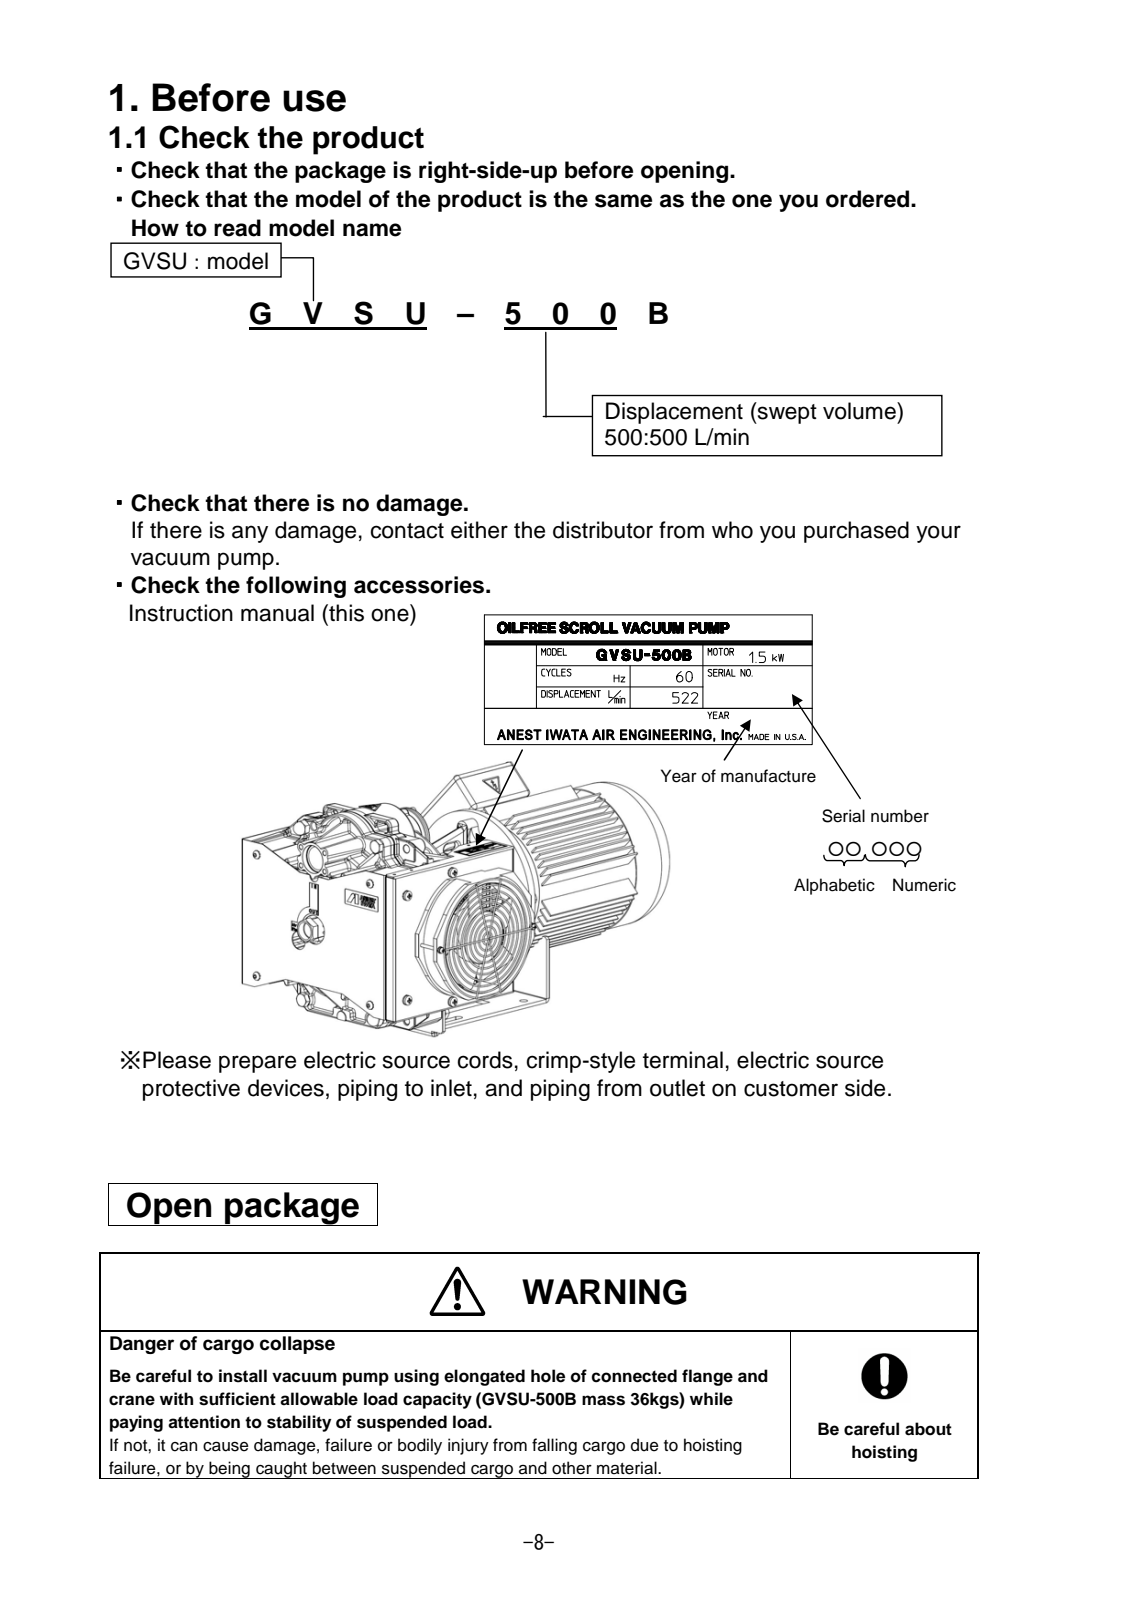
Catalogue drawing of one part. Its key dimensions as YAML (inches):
part_name: "GVSU-500B"
step_written_by: "SolidWorks 2018 (CONFIG_CONTROL_DESIGN)"
units: inches
bodies: {solids: 3, faces: 130, planar: 95, cylindrical: 20, other: 15}
overall_size: [23.11, 12.559, 11.865]
volume: 1319
surface_area: 1235
round_holes:
  - {diameter: 0.709, count: 1}
  - {diameter: 0.906, count: 1}
  - {diameter: 1.417, count: 1}
round_bosses_or_shafts:
  - {diameter: 7.874, count: 1}
  - {diameter: 7.087, count: 1}
  - {diameter: 6.772, count: 1}
  - {diameter: 6.299, count: 1}
partial_cylinders:
  - {radius: 0.197, count: 4}
  - {radius: 3.15, count: 1}
face_to_face_distances: [6.378, 0.236, 0.472, 0.866, 0.63, 1.89, 12.559, 4.488, 10.748, 1.811]
hole_center_spacings: [1.268, 3.622, 4.488]
